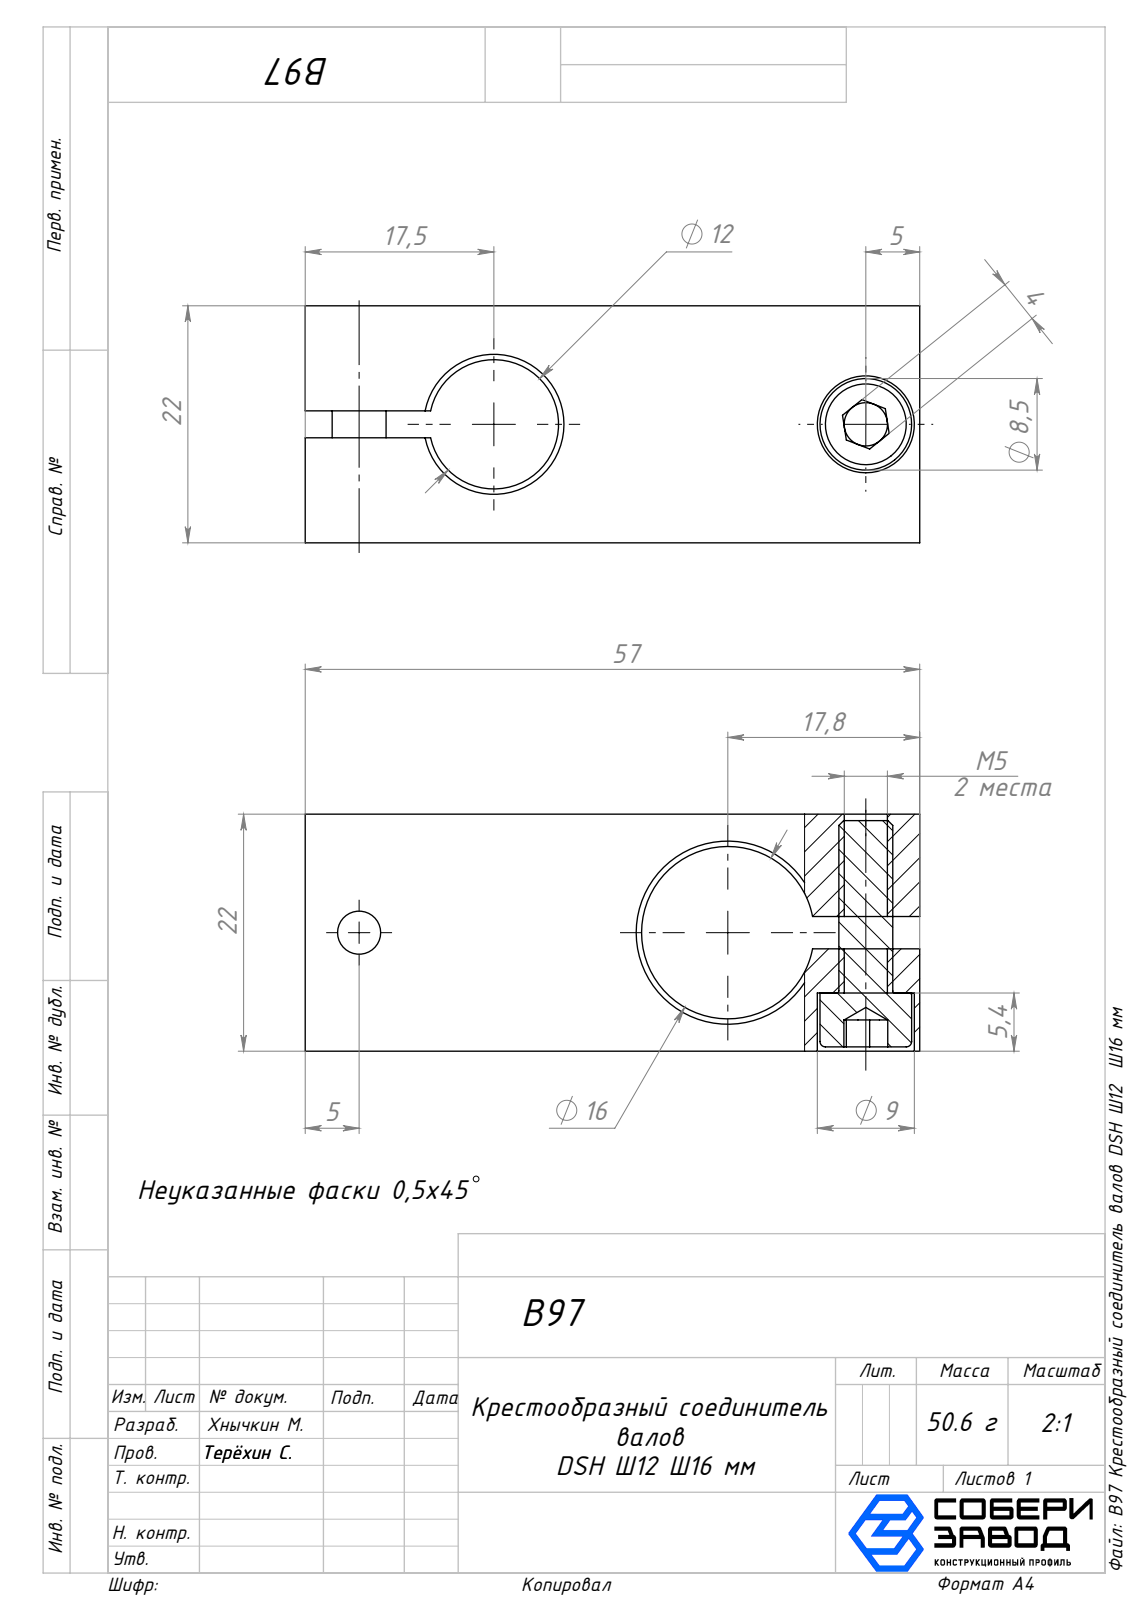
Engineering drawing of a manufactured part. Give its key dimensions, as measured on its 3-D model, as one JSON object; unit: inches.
{"part_name": "socket head cap screw_din_DIN 912 M5 x 16 --- 16N; B97 Крестообразный соединитель валов DSH Ø12 Ø16 мм_00; B97 Крестообразный соединитель валов DSH Ø12 Ø16 мм", "step_written_by": "SolidWorks 2025 (AUTOMOTIVE_DESIGN)", "units": "inches", "bodies": {"solids": 3, "faces": 92, "planar": 44, "cylindrical": 23, "other": 25}, "overall_size": [2.244, 0.866, 0.866], "volume_in3": 1.187, "surface_area_in2": 14.62, "round_holes": [[0.157, 2], [0.354, 2], [0.472, 1], [0.63, 1]], "round_bosses_or_shafts": [[0.335, 2], [0.197, 2]], "face_to_face_distances": [0.866, 0.384, 0.482, 2.244, 0.374, 0.492, 0.098, 0.118, 0.213, 0.654], "hole_center_spacings": [1.346, 1.358]}
